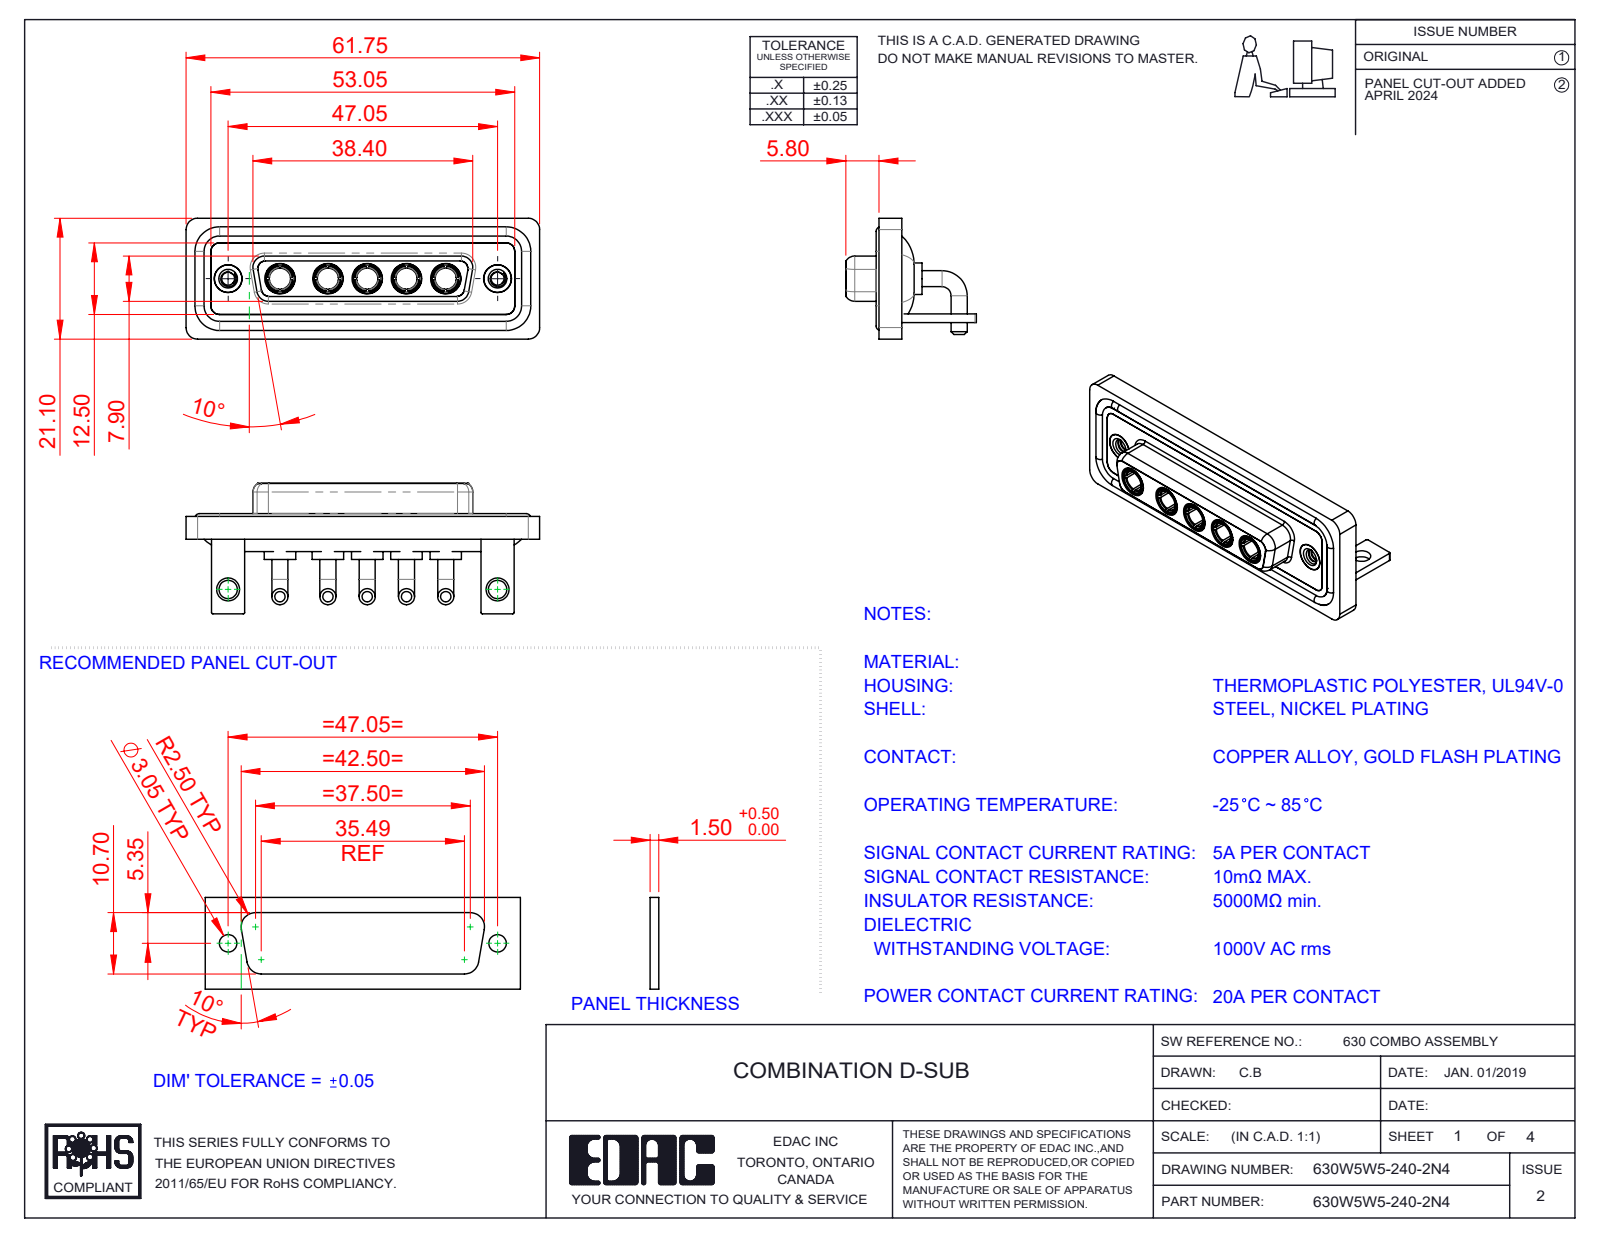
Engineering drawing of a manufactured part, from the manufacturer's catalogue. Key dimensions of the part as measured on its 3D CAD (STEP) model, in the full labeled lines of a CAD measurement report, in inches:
Part name (STEP PRODUCT): 630Combo Housing_5W5; 630Combo Shell Front_25 Contacts; 630Combo Threaded Rivet_2; Power Socket_20A RA (+4 more)
STEP written by: SolidWorks 2023 (CONFIG_CONTROL_DESIGN)
Units: inches
Bodies: 19 solids, 824 faces (270 planar, 337 cylindrical, 217 other)
Overall size (bounding box): 2.431 × 0.898 × 0.831
Volume: 0.537 in³ · Surface area: 22.55 in²
Round holes (diameter × count): ⌀0.191 ×7, ⌀0.146 ×5, ⌀0.209 ×5, ⌀0.089 ×2, ⌀0.126 ×2, ⌀0.157 ×2, ⌀0.159 ×2, ⌀0.197 ×2
Round bosses / shafts (diameter × count): ⌀0.11 ×10, ⌀0.217 ×5, ⌀0.205 ×5, ⌀0.195 ×5, ⌀0.187 ×5, ⌀0.148 ×5, ⌀0.063 ×4, ⌀0.195 ×2
Partial cylindrical surfaces — rounded edges, fillets, slot ends (radius × count): R0.079 ×19, R0.059 ×18, R0.01 ×16, R0.053 ×8, R0.063 ×8, R0.02 ×5, R0.083 ×5, R0.024 ×4
Main face-to-face distances: 0.016, 0.071, 0.114, 0.146, 0.059, 0.161, 0.043, 0.055, 0.063, 0.098
Hole centre spacings: 0.27, 0.356, 1.496, 1.852, 0.27, 0.33, 0.54, 0.541
